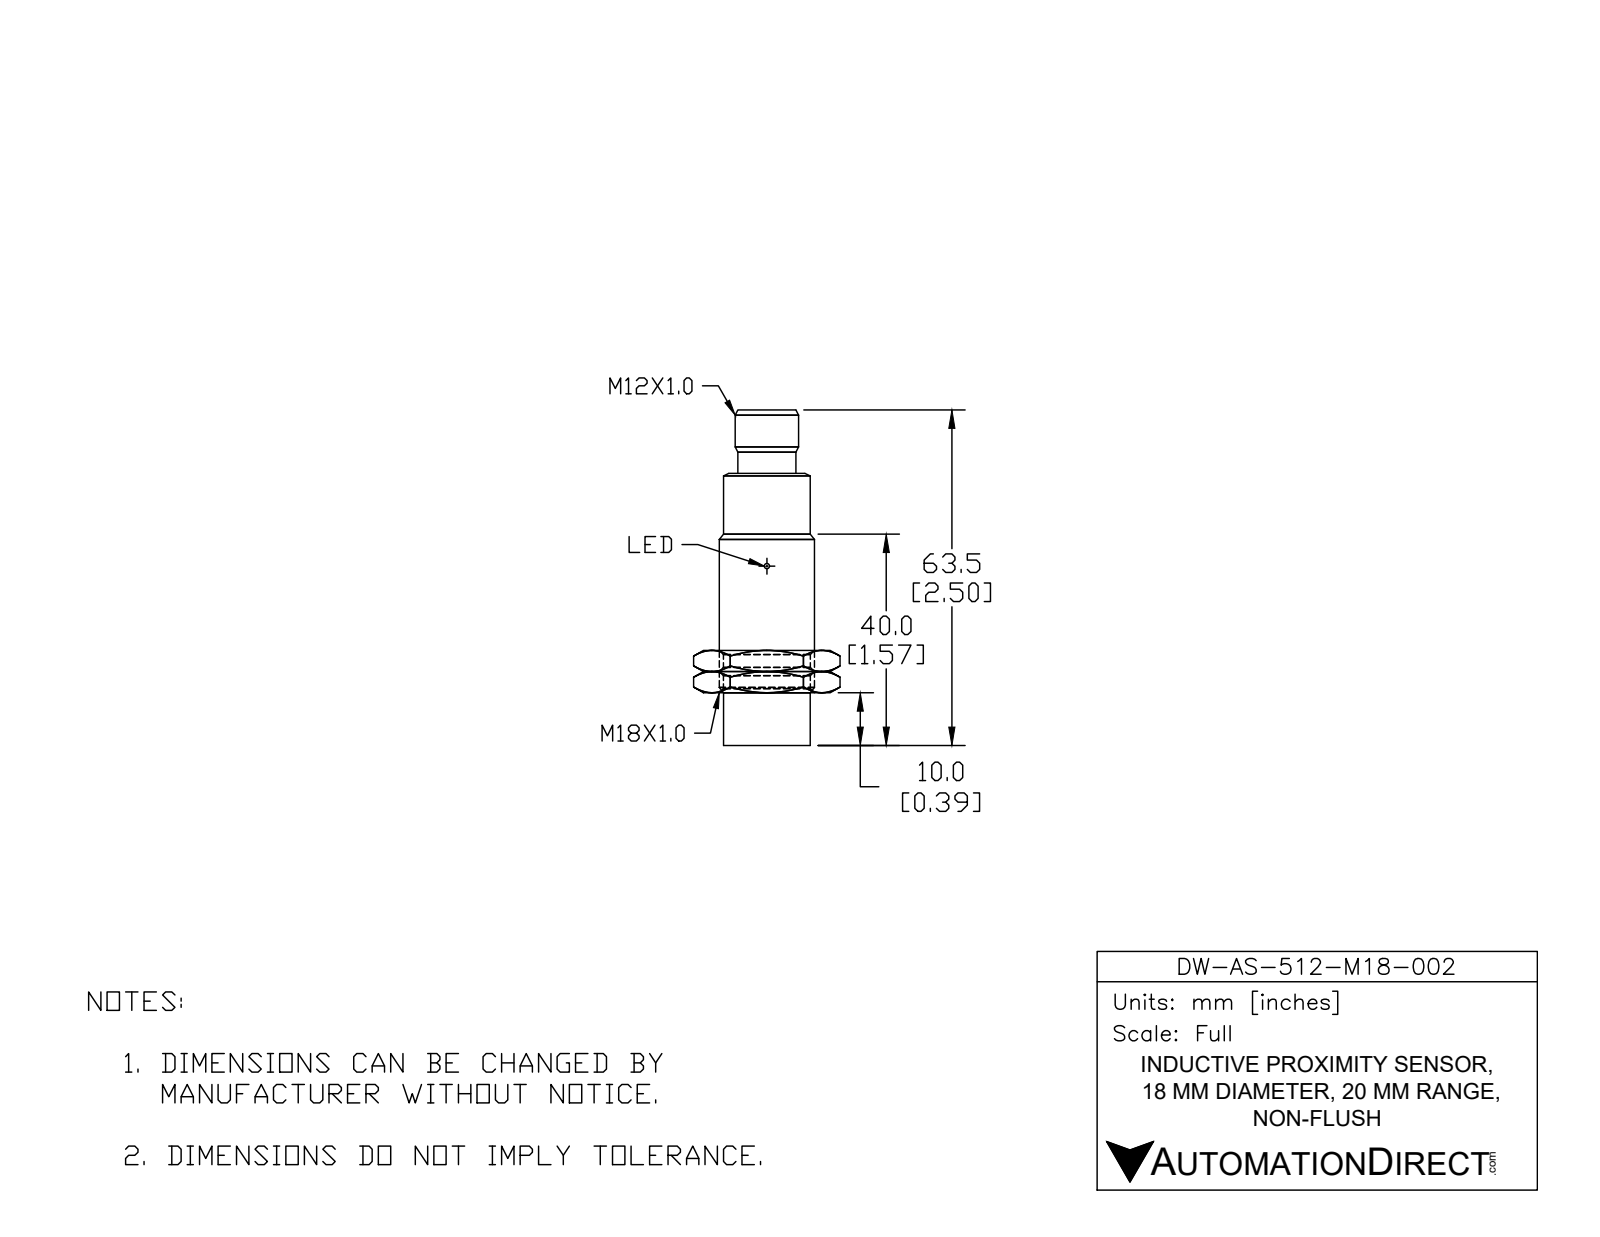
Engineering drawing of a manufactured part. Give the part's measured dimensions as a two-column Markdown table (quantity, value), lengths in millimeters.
| quantity | value |
| --- | --- |
| part name | DW-AS-512-M18-002 |
| STEP written by | SolidWorks 2017 (AUTOMOTIVE_DESIGN) |
| units | millimeters |
| bodies | 1 solid, 36 faces (13 planar, 14 cylindrical, 9 other) |
| overall size | 63.6 × 18 × 18 |
| volume | 12 800 mm³ |
| surface area | 4 146 mm² |
| round holes (diameter × count) | 3 × 2, 8.5 × 1 |
| round bosses / shafts (diameter × count) | 1.1 × 3, 18 × 1, 16.5 × 1, 16.4 × 1, 12 × 1, 10.5 × 1 |
| partial cylindrical surfaces (radius × count) | 0.5 × 2, 0.6 × 1 |
| main face-to-face distances | 50.5, 54.8, 4.3, 63.6, 13.1, 8.7, 42, 8.5, 12.9, 21.5 |
